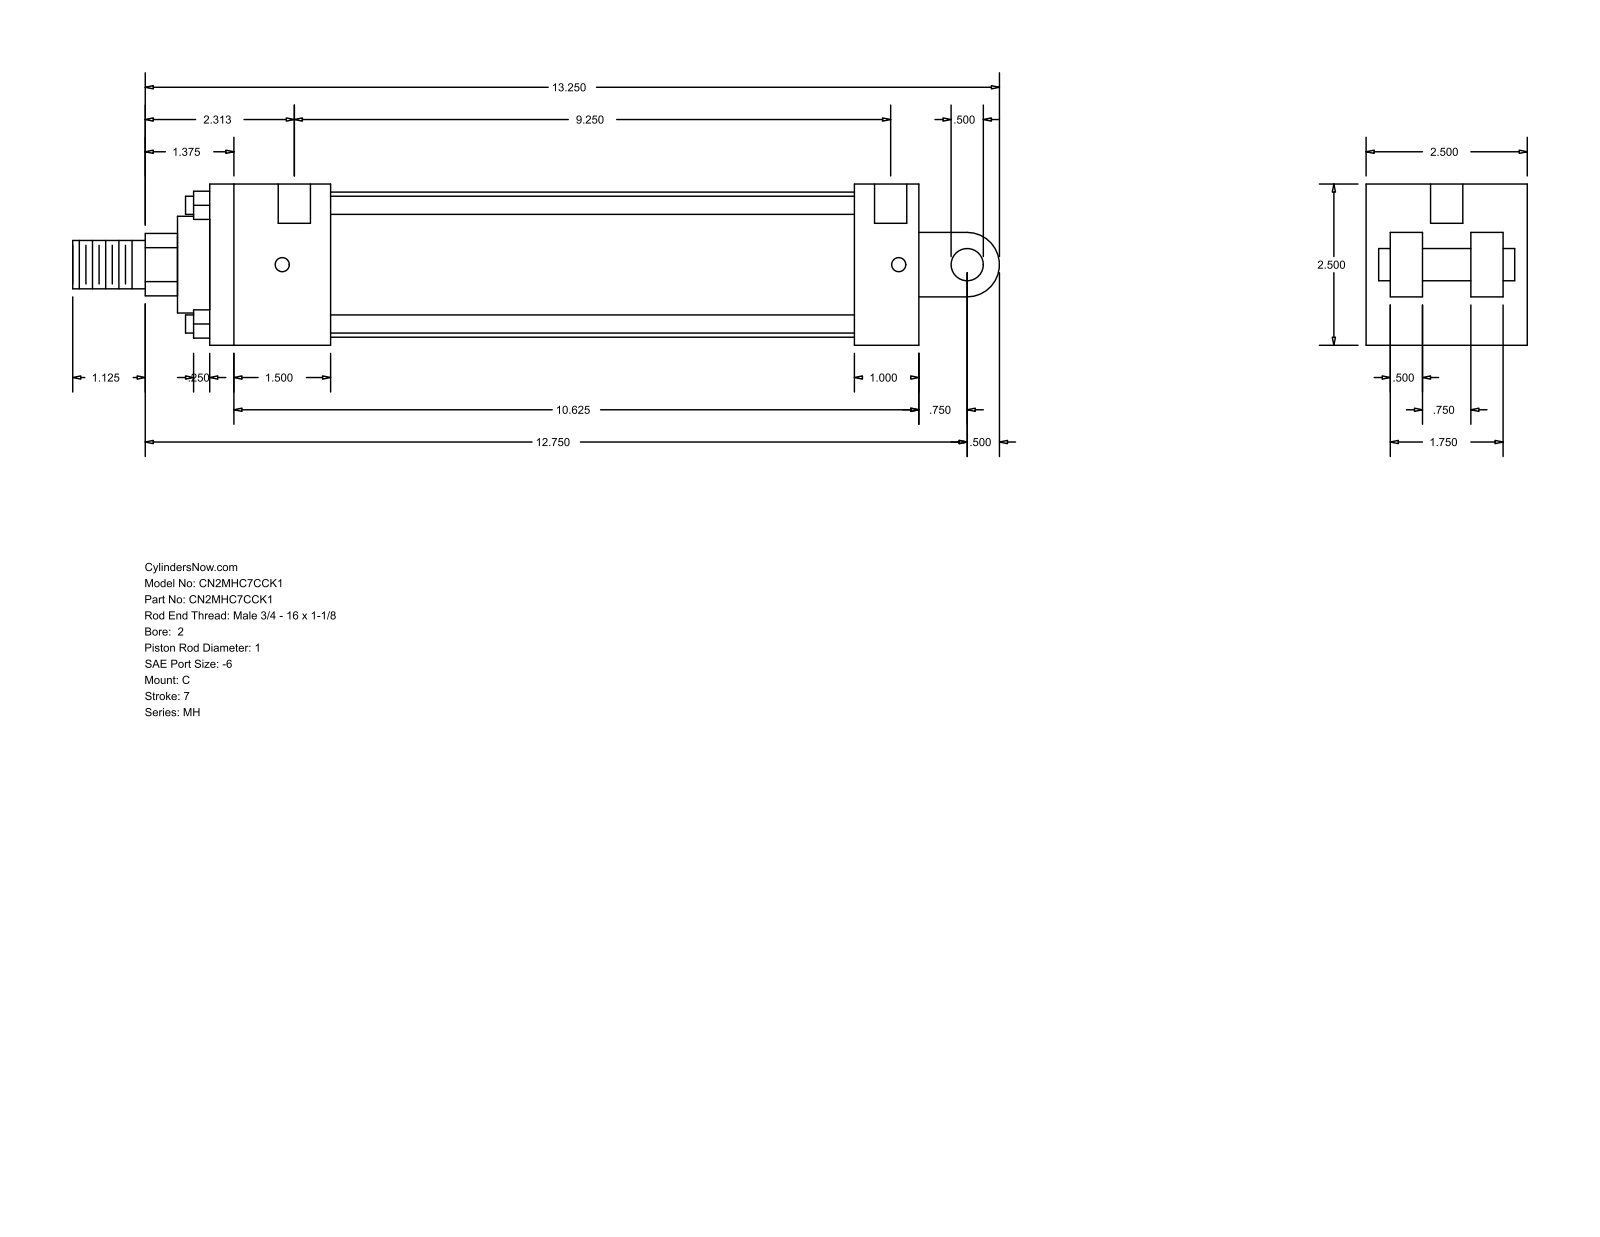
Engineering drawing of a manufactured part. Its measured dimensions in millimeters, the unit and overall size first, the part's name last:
Units: millimetres
Overall size (bounding box): 365.12 × 63.5 × 63.5
Round holes (diameter × count): ⌀5.56 ×4, ⌀12.7 ×2
Round bosses / shafts (diameter × count): ⌀7.14 ×4, ⌀57.15 ×1, ⌀38.1 ×1, ⌀25.4 ×1, ⌀19.05 ×1, ⌀12.7 ×1
Partial cylindrical surfaces — rounded edges, fillets, slot ends (radius × count): R12.29 ×1, R12.7 ×1
Main face-to-face distances: 63.5, 279.4, 12.7, 25.4, 47.63, 53.98, 9.52, 254, 206.37, 231.77
Hole centre spacings: 242.88, 3.17, 4.76, 234.95, 238.12, 239.71
Bodies: 0 solids, 99 faces (70 planar, 29 cylindrical, 0 other)
Part name (STEP PRODUCT): MH_C__0200_1
STEP written by: GSSL Pune (CONFIG_CONTROL_DESIGN)
